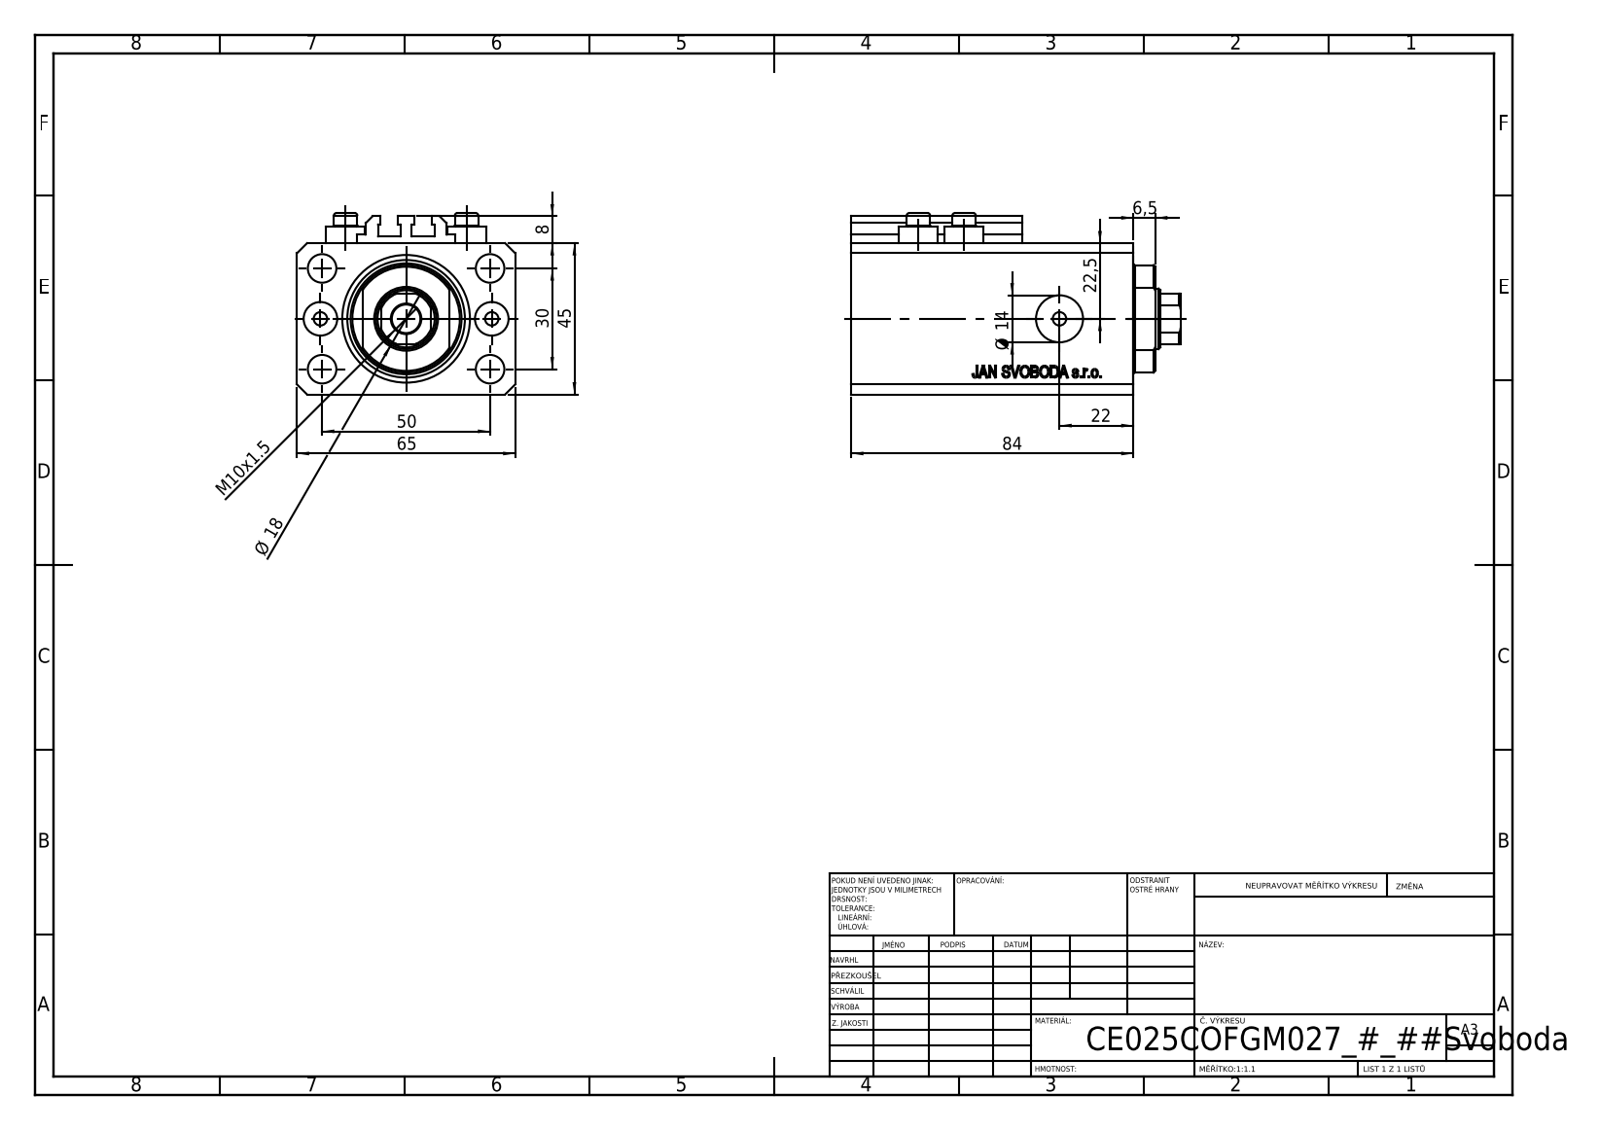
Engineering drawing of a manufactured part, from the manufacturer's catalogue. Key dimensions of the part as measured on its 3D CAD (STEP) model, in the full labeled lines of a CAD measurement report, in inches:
Part name (STEP PRODUCT): V250CE_C_VCP; ALLEN BOLT V250CE; V250CE_VC_C; V250CE_C_Body
STEP written by: SolidWorks 2019 (CONFIG_CONTROL_DESIGN)
Units: inches
Bodies: 8 solids, 1034 faces (504 planar, 86 cylindrical, 444 other)
Overall size (bounding box): 3.858 × 2.559 × 2.126
Volume: 14.03 in³ · Surface area: 94.79 in²
Round holes (diameter × count): ⌀0.157 ×8, ⌀0.335 ×5, ⌀0.394 ×2, ⌀0.551 ×2, ⌀0.709 ×1, ⌀0.984 ×1, ⌀1.496 ×1
Round bosses / shafts (diameter × count): ⌀0.457 ×4, ⌀0.276 ×4
Partial cylindrical surfaces — rounded edges, fillets, slot ends (radius × count): R0.008 ×10, R0.335 ×1, R0.63 ×1
Main face-to-face distances: 1.772, 2.559, 0.551, 2.756, 3.307, 1.85, 0.272, 2.484, 3.035, 0.118
Hole centre spacings: 0.591, 1.148, 2.074, 0.535, 1.004, 1.181, 1.417, 1.515
